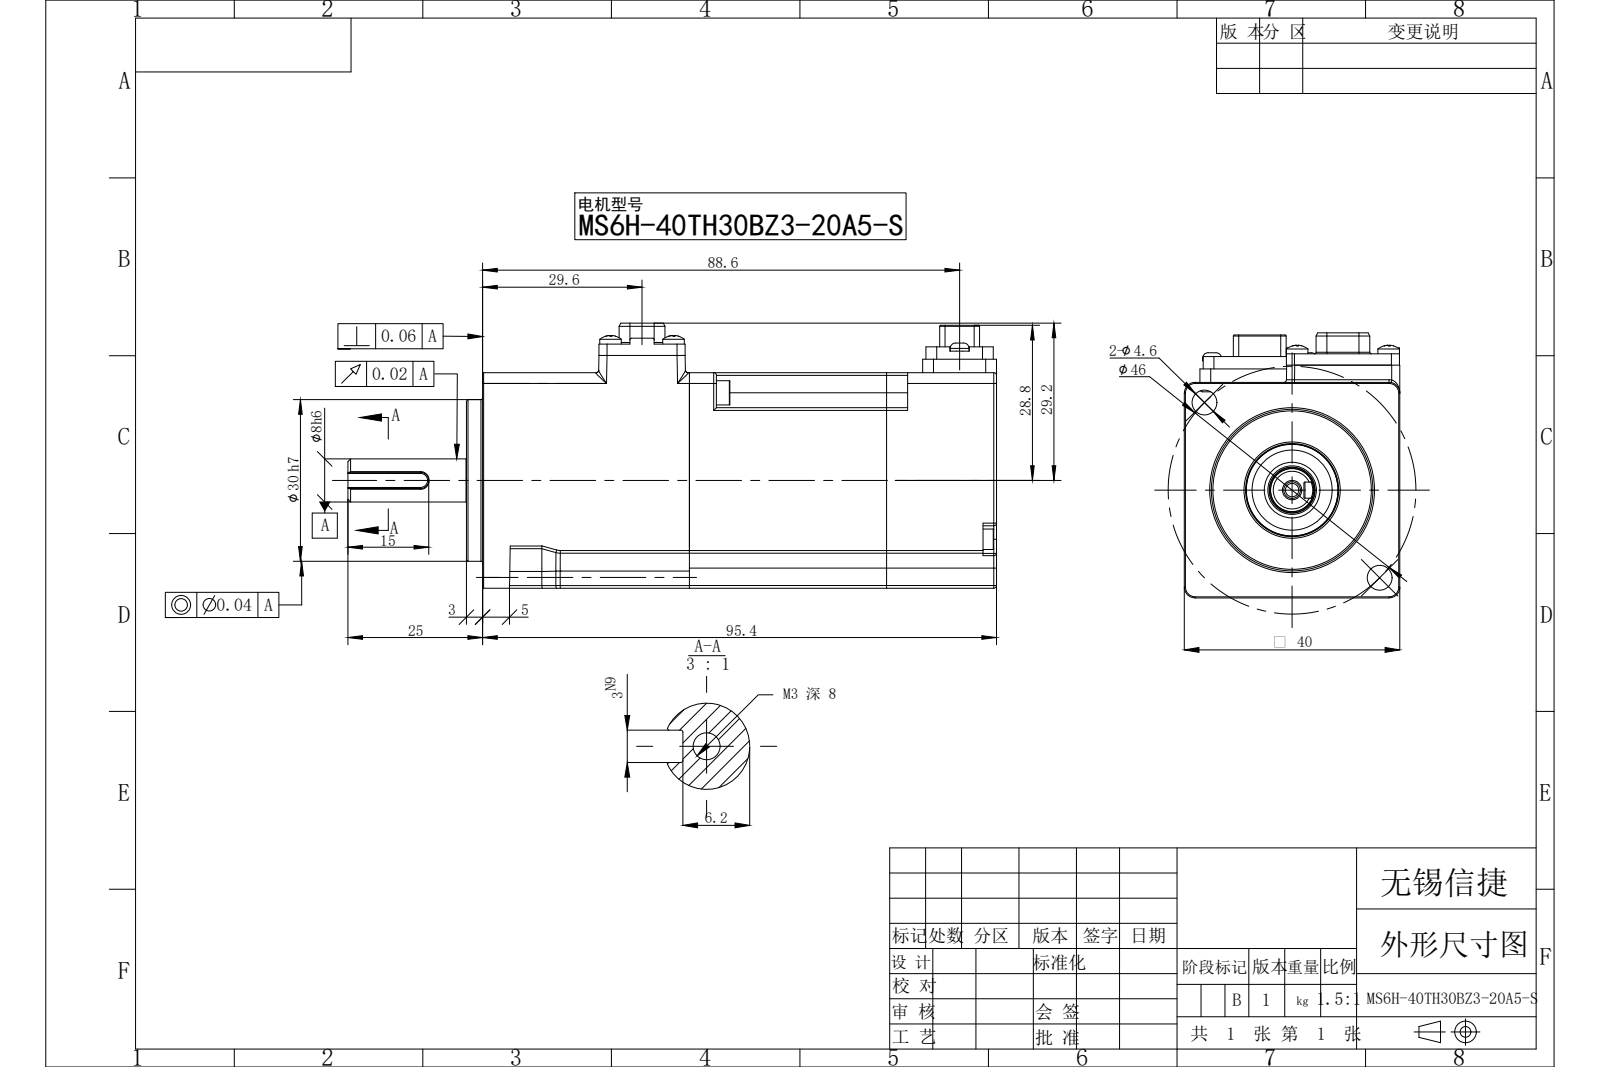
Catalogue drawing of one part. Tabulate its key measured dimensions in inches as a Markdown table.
| quantity | value |
| --- | --- |
| part name | MS6H-40TH30BZ3-20A5-S |
| STEP written by | SolidWorks 2022 (CONFIG_CONTROL_DESIGN) |
| units | inches |
| bodies | 0 solids, 705 faces (374 planar, 216 cylindrical, 115 other) |
| overall size | 4.74 × 1.937 × 1.575 |
| round holes (diameter × count) | 0.083 × 4, 0.063 × 2, 0.181 × 2, 0.098 × 1, 0.354 × 1, 0.585 × 1 |
| round bosses / shafts (diameter × count) | 0.157 × 4, 0.15 × 4, 0.177 × 2, 0.138 × 2, 1.181 × 1, 0.669 × 1, 0.407 × 1, 0.335 × 1 |
| partial cylindrical surfaces (radius × count) | 0.02 × 60, 0.008 × 16, 0.079 × 16, 0.012 × 10, 0.059 × 9, 0.039 × 4, 0.098 × 4, 0.109 × 4 |
| main face-to-face distances | 1.575, 0.256, 1.319, 3.756, 1.512, 2.244, 1.063, 1.63, 0.118, 3.874 |
| hole center spacings | 0.315, 0.654, 0.726, 0.906, 0.669, 1.811, 2.164, 2.245 |
